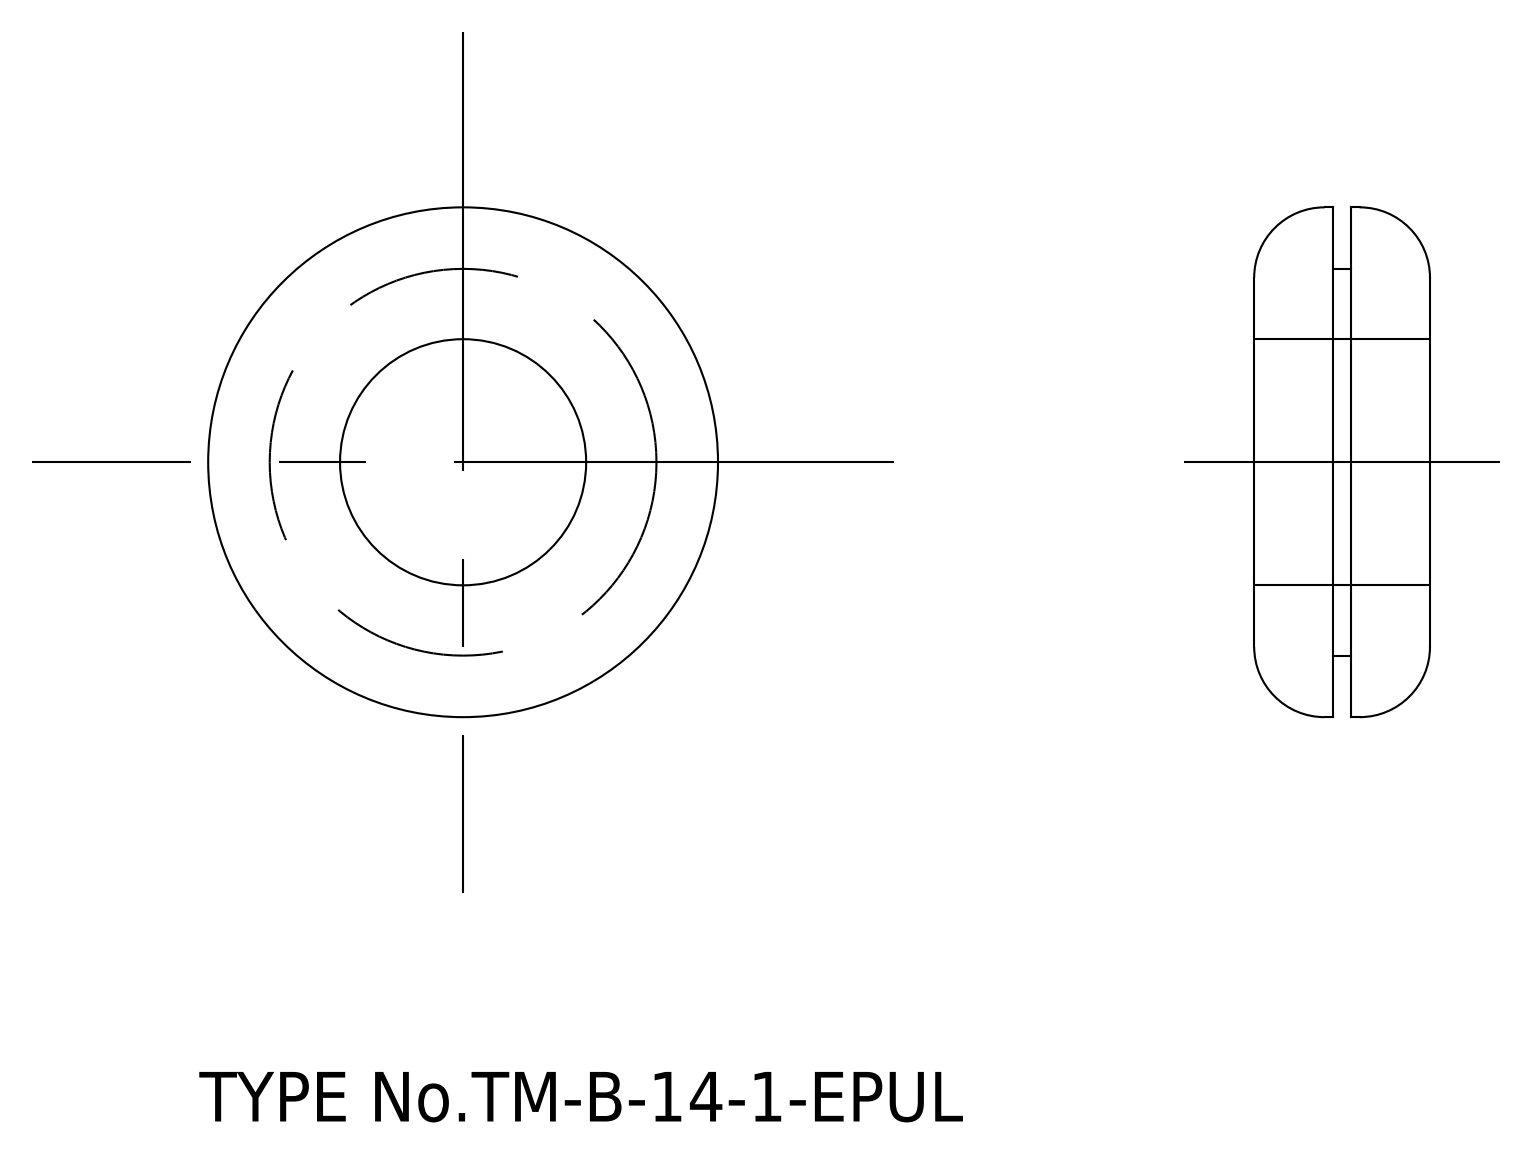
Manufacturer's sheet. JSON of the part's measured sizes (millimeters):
{"step_written_by": "spGate 15.6.1 (AUTOMOTIVE_DESIGN)", "units": "millimeters", "bodies": {"solids": 1, "faces": 16, "planar": 4, "cylindrical": 8, "other": 4}, "overall_size": [29, 29, 10], "volume_mm3": 4200, "surface_area_mm2": 2576, "round_holes": [[14, 1]], "round_bosses_or_shafts": [[29, 1], [22, 1]], "face_to_face_distances": [4.5, 5.5, 1, 10]}
